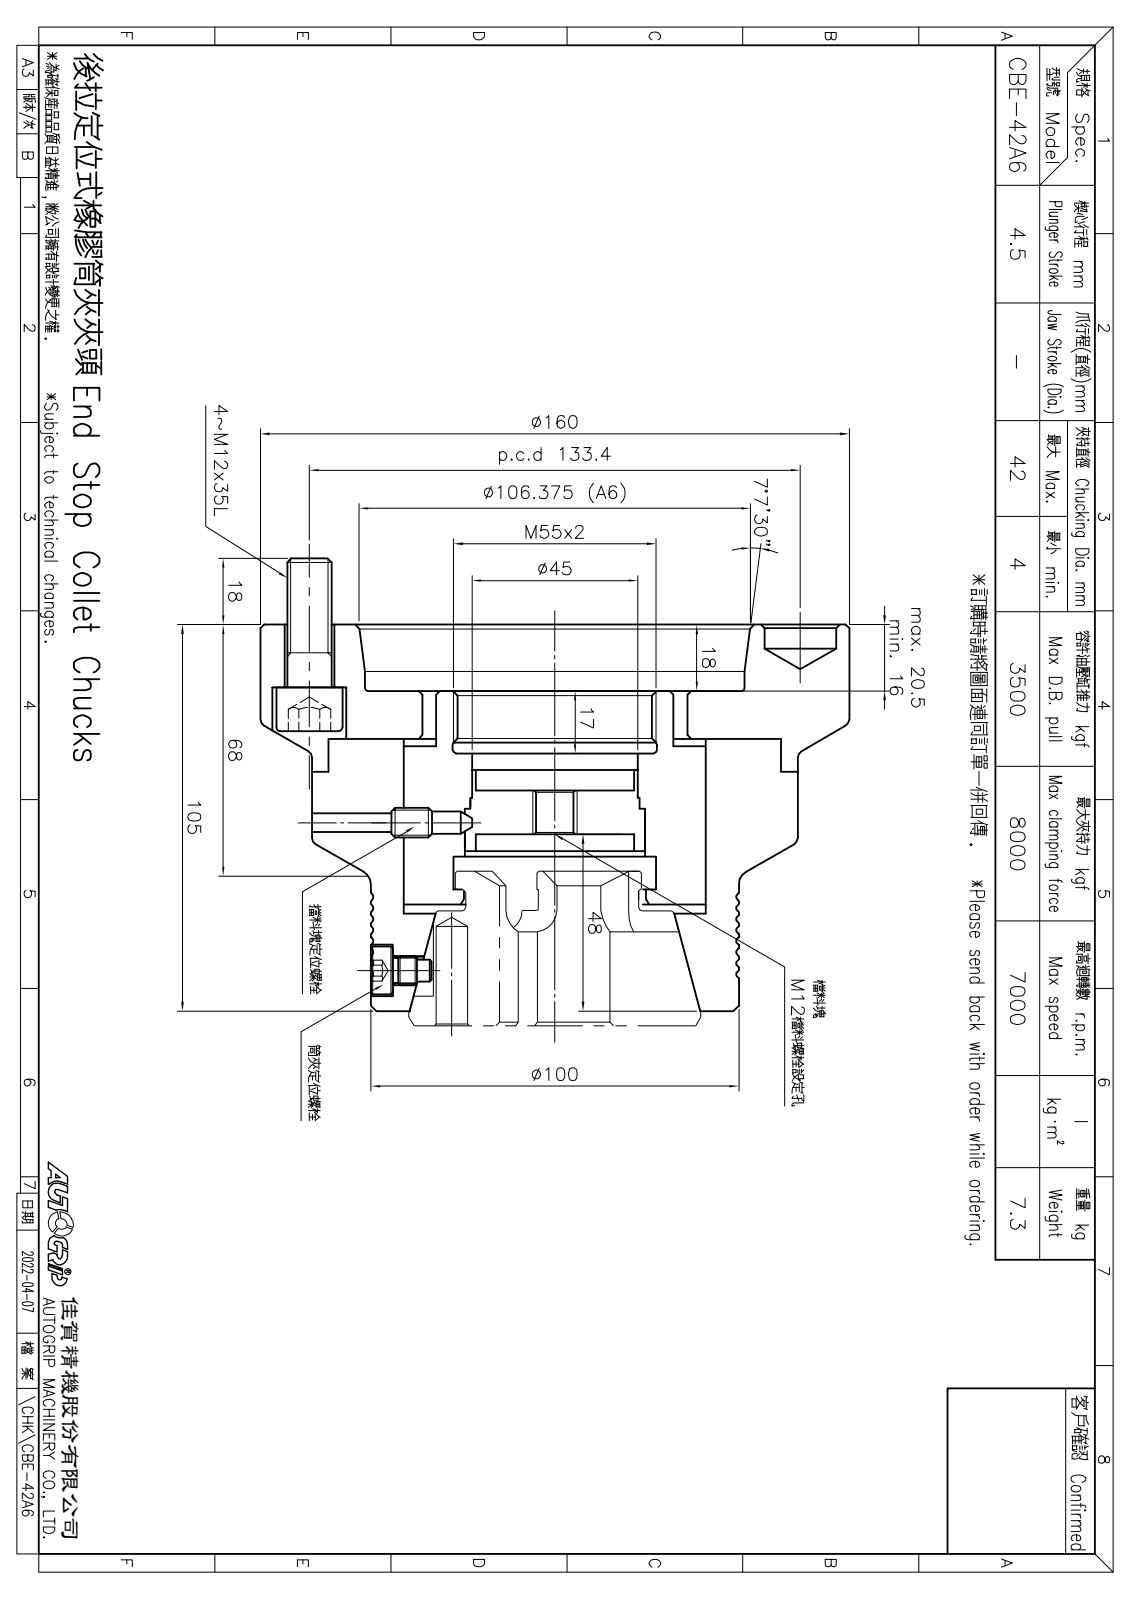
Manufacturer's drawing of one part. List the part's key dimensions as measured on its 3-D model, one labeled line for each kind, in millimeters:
Part name (STEP PRODUCT): CF-CBE-42-03010; CF-CBE-42-01010; 圓頭內六角螺栓_M12x35; CF-CBE-42A6-01010 (+2 more)
STEP written by: SolidWorks 2016 (CONFIG_CONTROL_DESIGN)
Units: millimetres
Bodies: 8 solids, 353 faces (95 planar, 100 cylindrical, 158 other)
Overall size (bounding box): 160 × 160 × 123
Volume: 992 199 mm³ · Surface area: 177 068 mm²
Round holes (diameter × count): ⌀13.5 ×4, ⌀20 ×4, ⌀19.4 ×2, ⌀10.2 ×1, ⌀43 ×1, ⌀45 ×1, ⌀49 ×1, ⌀49.5 ×1, ⌀55 ×1, ⌀55.5 ×1, ⌀72 ×1, ⌀82 ×1
Round bosses / shafts (diameter × count): ⌀18 ×4, ⌀12 ×4, ⌀160 ×1, ⌀132 ×1, ⌀100 ×1, ⌀64.5 ×1
Main face-to-face distances: 31, 18, 13, 45, 17, 76, 58, 12, 40, 22
Hole centre spacings: 66.7, 94.33, 34.53, 115.53, 128.85, 133.4, 133.39
